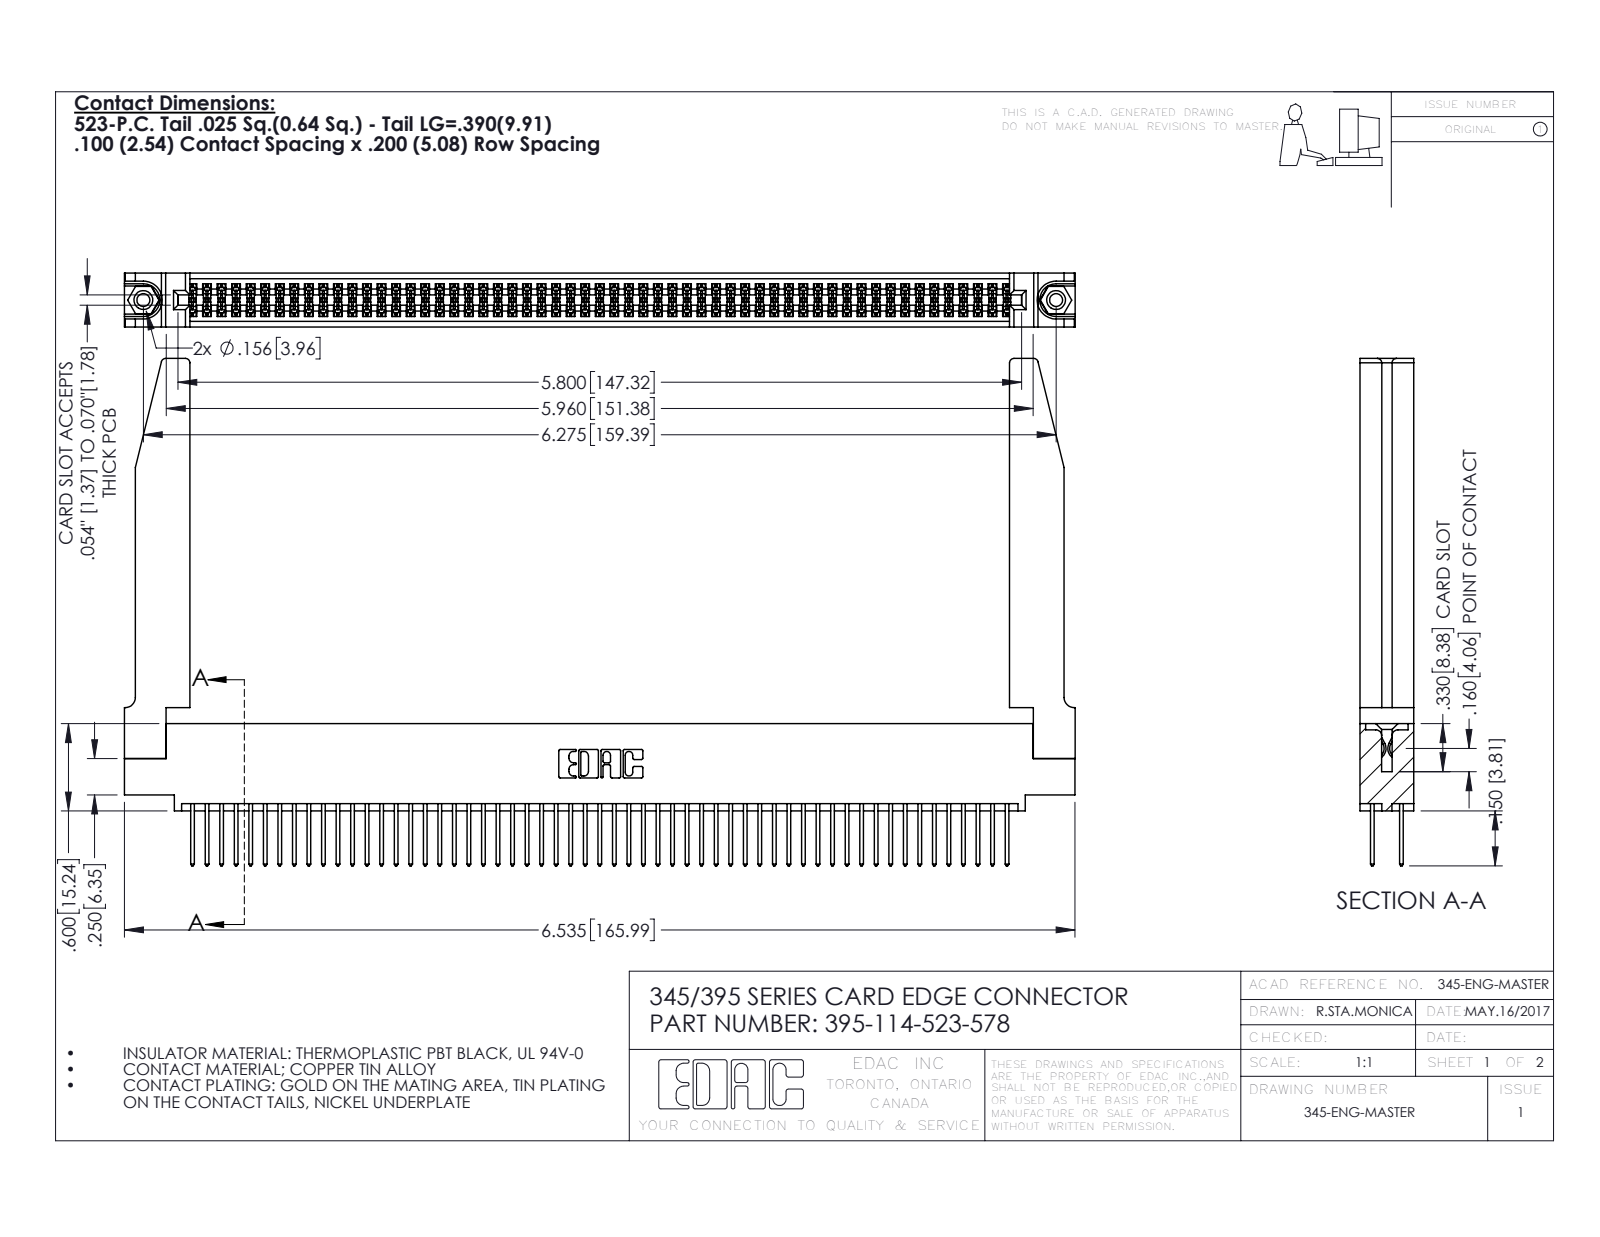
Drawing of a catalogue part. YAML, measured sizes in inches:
part_name: "345 Part_0.110 Offset - 0.156 Dia-TH; 345-250-001_345-250-001-102; 345-220-078_345-220-078; 395-114-523-578 (+1 more)"
step_written_by: "SolidWorks 2016 (CONFIG_CONTROL_DESIGN)"
units: inches
bodies: {solids: 119, faces: 6064, planar: 3988, cylindrical: 2024, other: 52}
overall_size: [6.536, 3.487, 0.37]
volume: 1.477
surface_area: 50.45
round_holes:
  - {diameter: 0.089, count: 2}
  - {diameter: 0.125, count: 2}
  - {diameter: 0.156, count: 2}
  - {diameter: 0.064, count: 1}
round_bosses_or_shafts:
  - {diameter: 0.155, count: 2}
partial_cylinders:
  - {radius: 0.006, count: 171}
  - {radius: 0.01, count: 114}
  - {radius: 0.01, count: 22}
  - {radius: 0.03, count: 8}
  - {radius: 0.007, count: 6}
  - {radius: 0.031, count: 6}
  - {radius: 0.026, count: 3}
  - {radius: 0.014, count: 2}
face_to_face_distances: [0.072, 0.298, 0.37, 0.2, 0.098, 0.272, 0.025, 0.225, 0.175, 0.148]
hole_center_spacings: [0.27, 6.039, 6.275]
